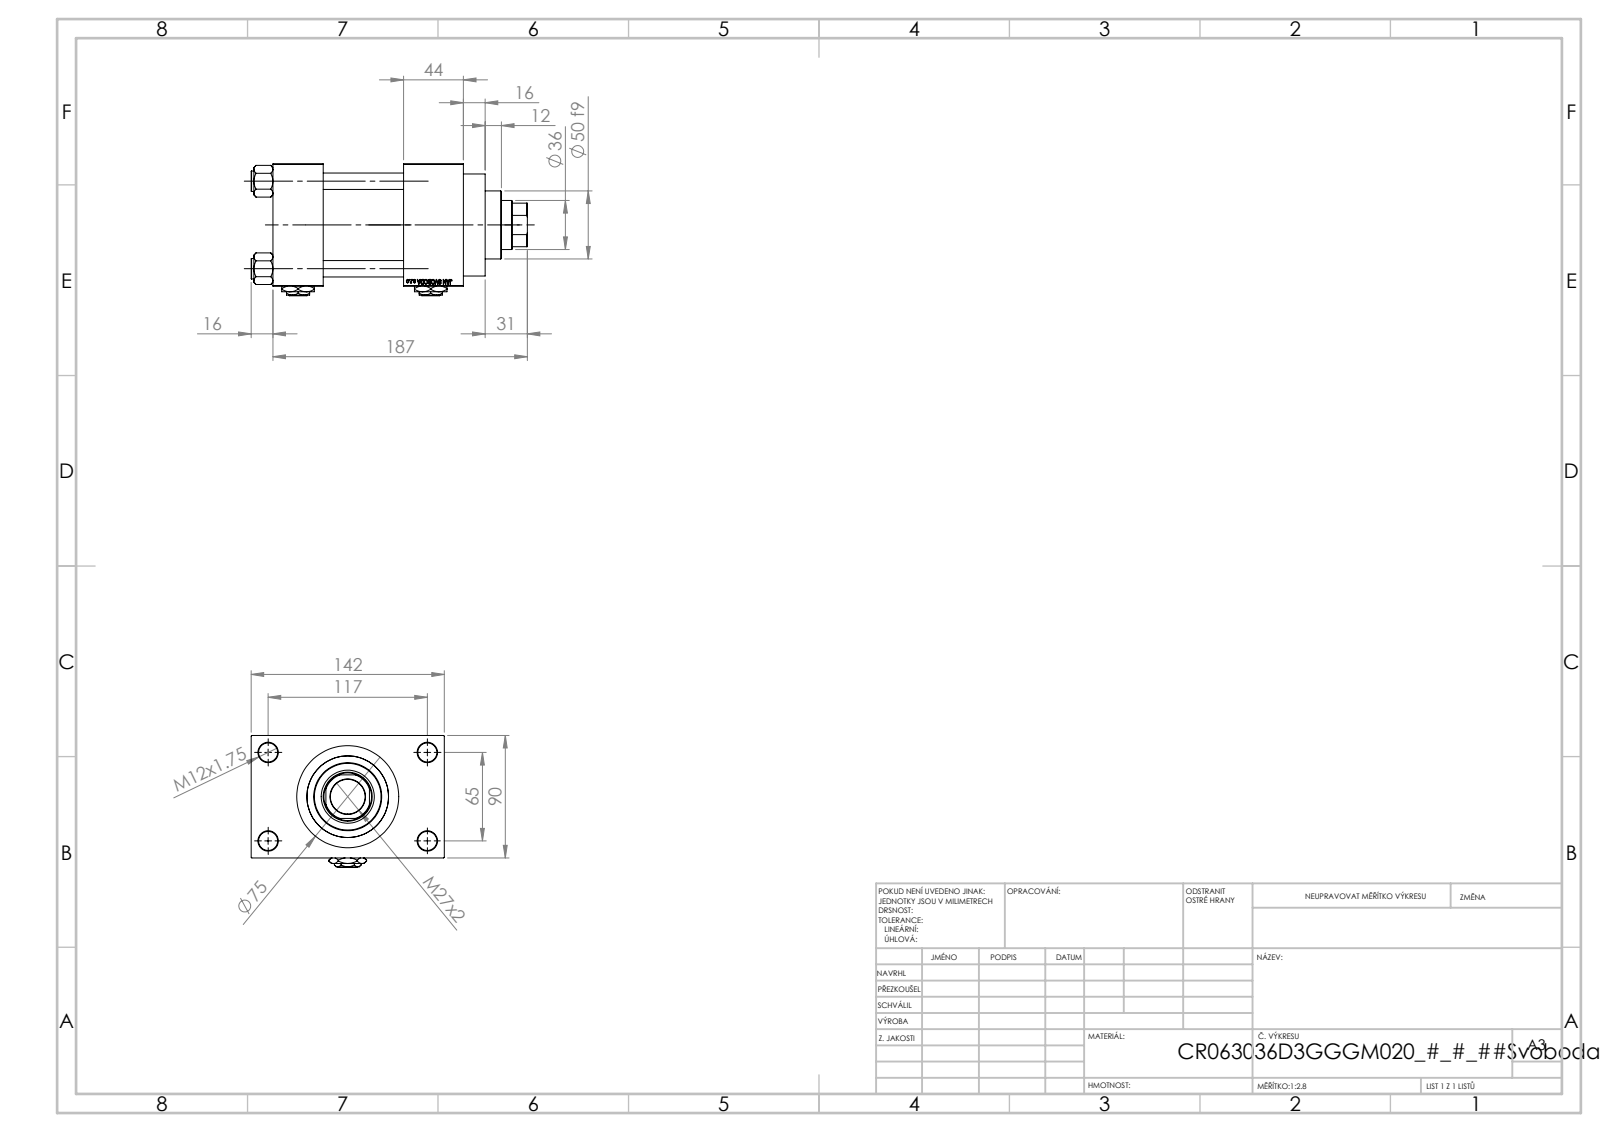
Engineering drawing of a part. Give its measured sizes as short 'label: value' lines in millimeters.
name: V215CR_D_Body; V215CR_D_TYCINKA; Zatka_pro_OIL_PORT; NUT_M5_D (+2 more)
written by: SolidWorks 2019 (CONFIG_CONTROL_DESIGN)
unit: mm
bodies: 13 solids, 1205 faces (545 planar, 100 cylindrical, 560 other)
size: 203 × 142 × 97
volume: 1 115 000 mm³; area: 208 707 mm²
holes: 4× ⌀12, 4× ⌀14, 2× ⌀7, 2× ⌀20.96, 2× ⌀30, 1× ⌀25.5, 1× ⌀36, 1× ⌀39, 1× ⌀50, 1× ⌀60, 1× ⌀63
bosses: 4× ⌀15, 1× ⌀75, 1× ⌀69
rounds: 1× R17.5
face distances: 90, 59, 37, 96, 140, 103, 44, 26, 116, 142
hole spacings: 26.35, 45.47, 64.3, 66.92, 69.81, 90.65, 111.34, 65
